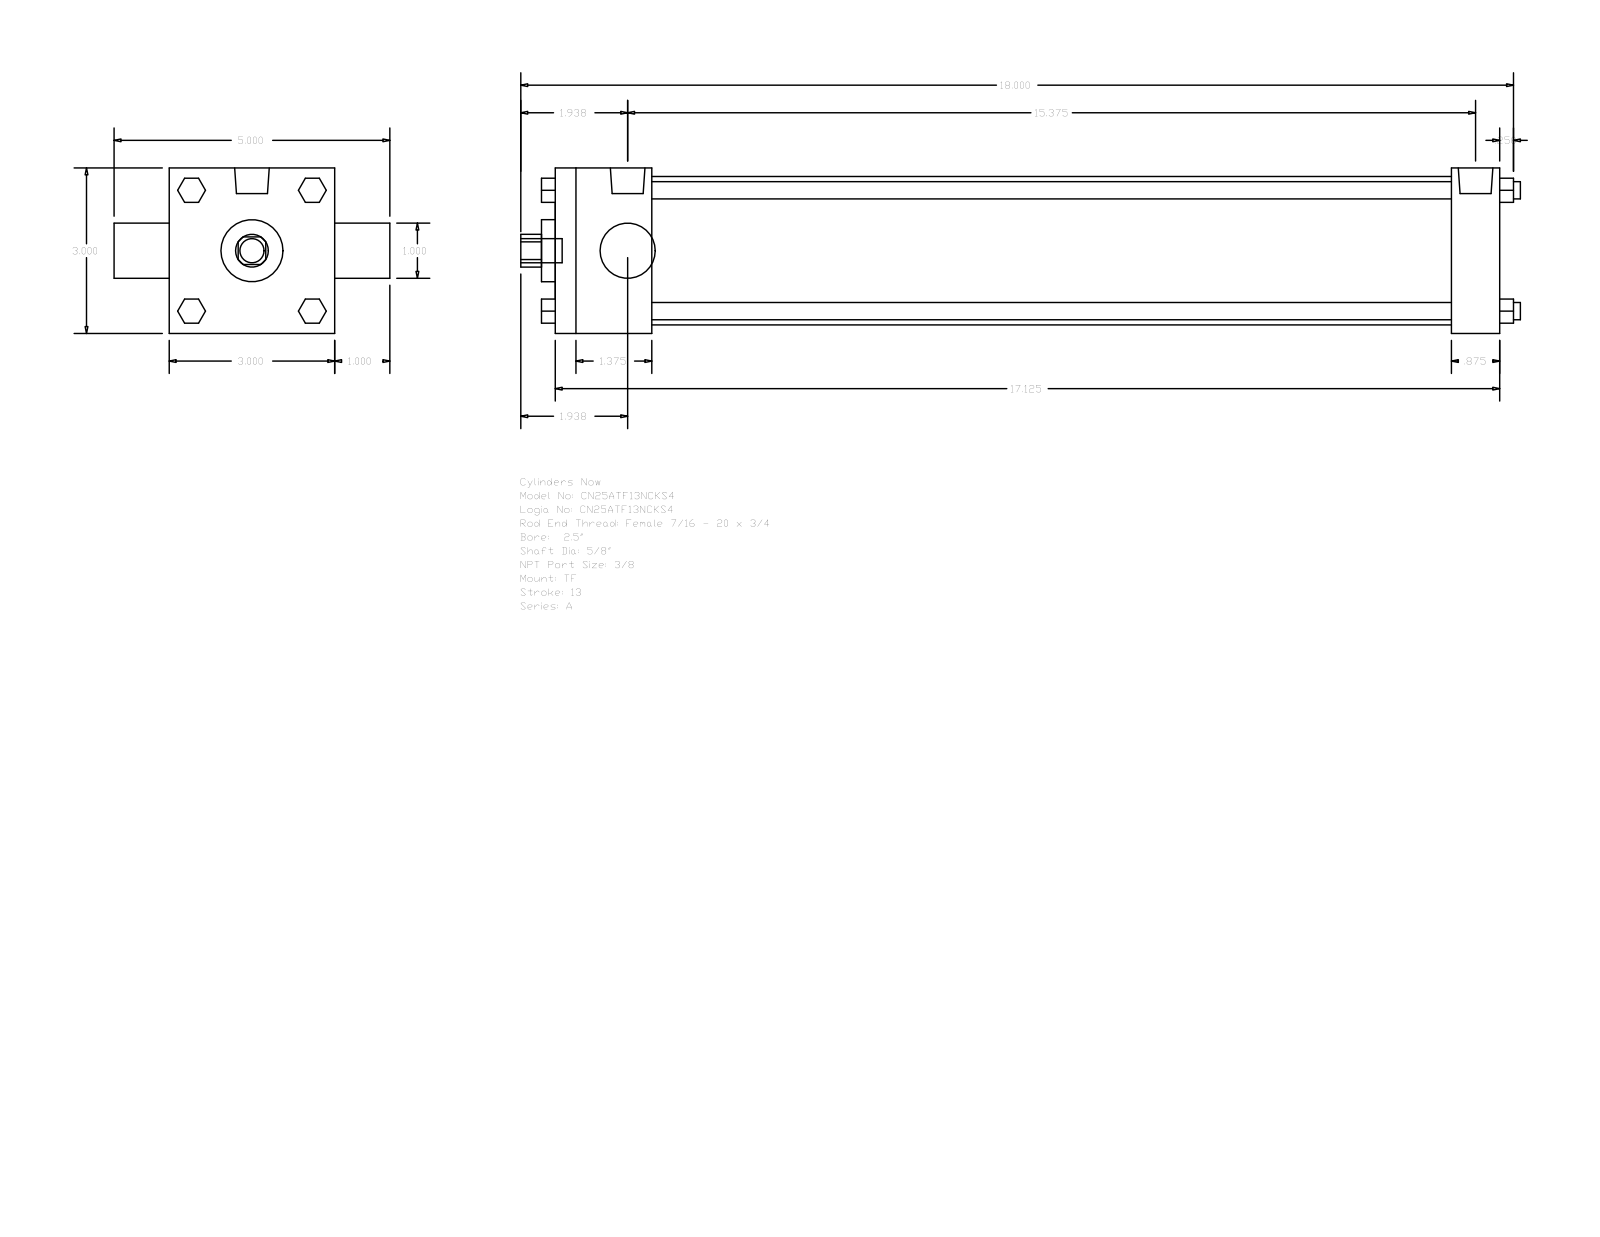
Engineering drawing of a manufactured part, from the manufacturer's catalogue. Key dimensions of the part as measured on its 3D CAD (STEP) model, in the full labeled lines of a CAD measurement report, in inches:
Part name (STEP PRODUCT): A_TF__0250_0.625
STEP written by: GSSL Pune (CONFIG_CONTROL_DESIGN)
Units: inches
Bodies: 0 solids, 120 faces (92 planar, 28 cylindrical, 0 other)
Overall size (bounding box): 18.125 × 5 × 3
Round holes (diameter × count): ⌀0.625 ×1, ⌀1 ×1, ⌀1.125 ×1, ⌀2.69 ×1
Round bosses / shafts (diameter × count): ⌀0.313 ×4, ⌀0.219 ×3, ⌀0.627 ×2, ⌀0.437 ×1
Partial cylindrical surfaces — rounded edges, fillets, slot ends (radius × count): R0.297 ×1
Main face-to-face distances: 3, 17.125, 1.75, 16.25, 14.5, 15.375, 0.875, 1, 4, 0.25
